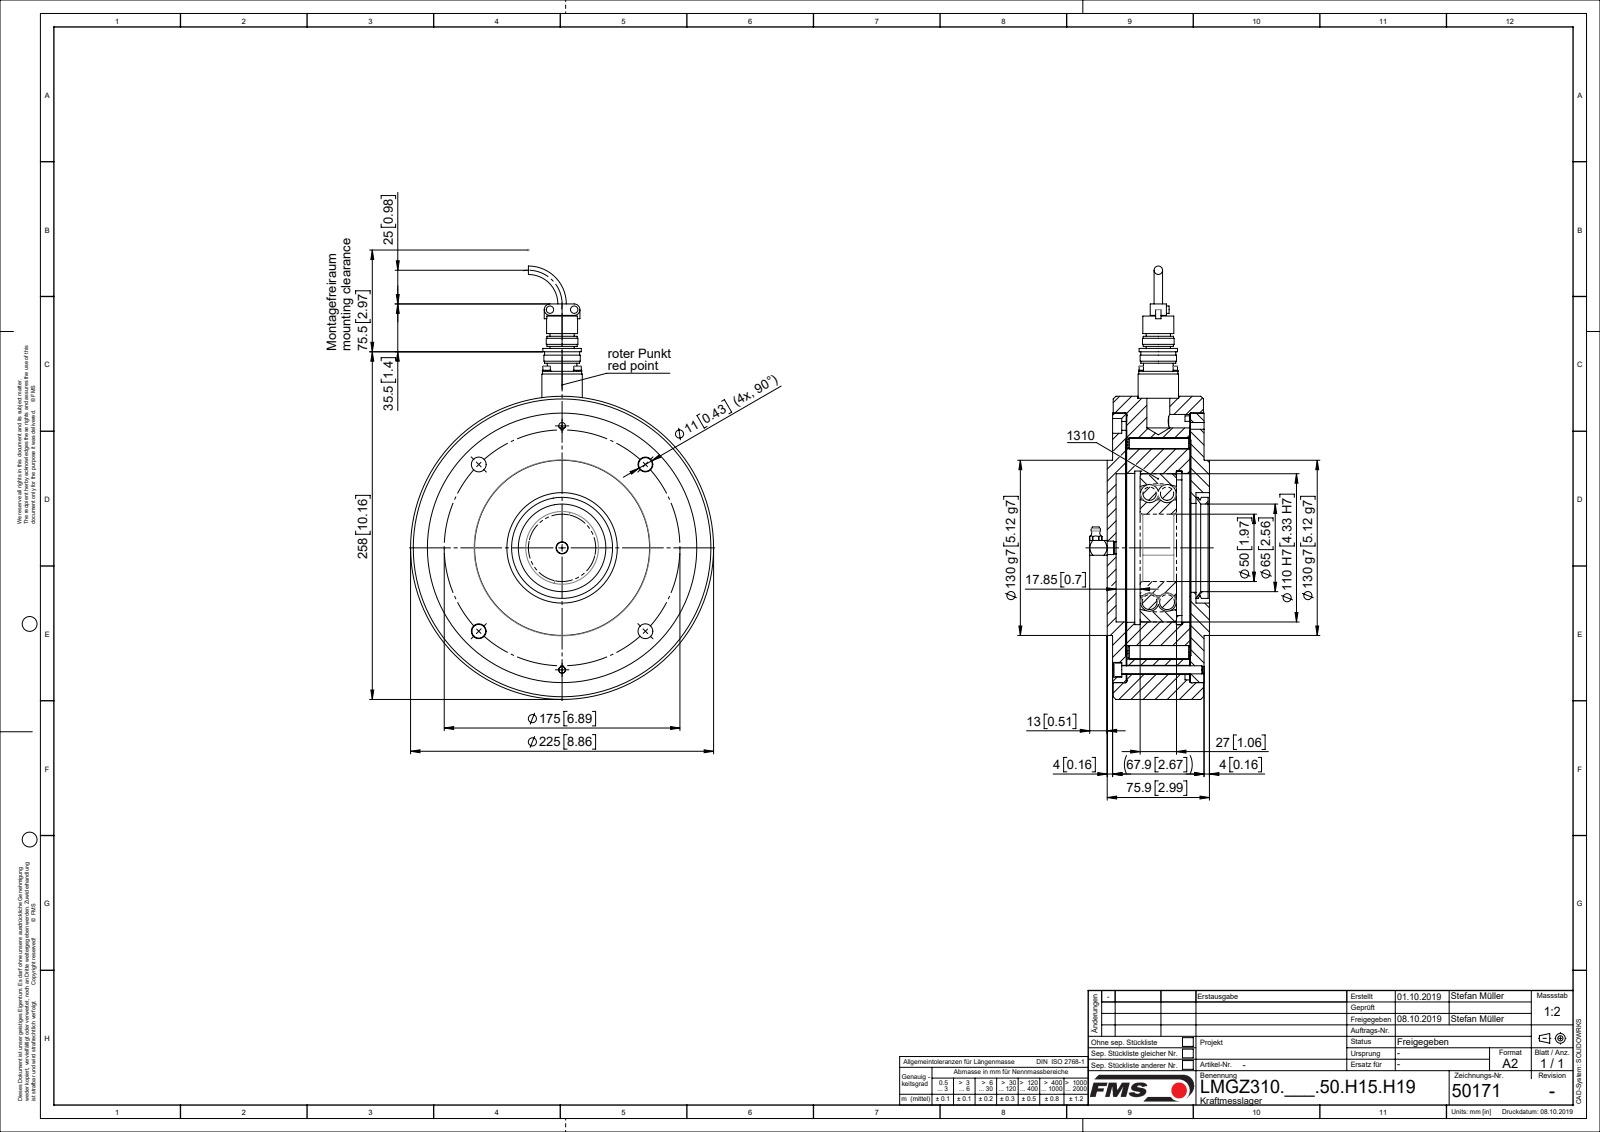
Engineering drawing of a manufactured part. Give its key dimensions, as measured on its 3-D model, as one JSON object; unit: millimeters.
{"part_name": "L50171; L49380; TEIL1; L49026 (+8 more)", "step_written_by": "Mechanical Desktop 2007 (CONFIG_CONTROL_DESIGN)", "units": "millimeters", "bodies": {"solids": 20, "faces": 411, "planar": 119, "cylindrical": 232, "other": 60}, "overall_size": [321.65, 225, 126.8], "volume_mm3": 2406000, "surface_area_mm2": 389818, "round_holes": [[11, 6], [2.6, 4], [3.2, 4], [3.4, 4], [9, 4], [5, 2], [6.6, 2], [8.68, 1], [23, 1], [50, 1], [64, 1], [66, 1]], "round_bosses_or_shafts": [[5.5, 6], [6.2, 4], [3, 4], [2.5, 4], [10, 2], [225, 1], [199, 1], [130, 1]], "partial_cylinders_radius": [[4.25, 2], [81, 1], [86, 1]], "face_to_face_distances": [9.7, 47.25, 10.75, 47.45, 10.2, 10.45, 57.45, 57.7, 47, 10], "hole_center_spacings": [16.26, 23, 87.5, 32.53, 68.17, 68.18, 90.5, 123.74]}
